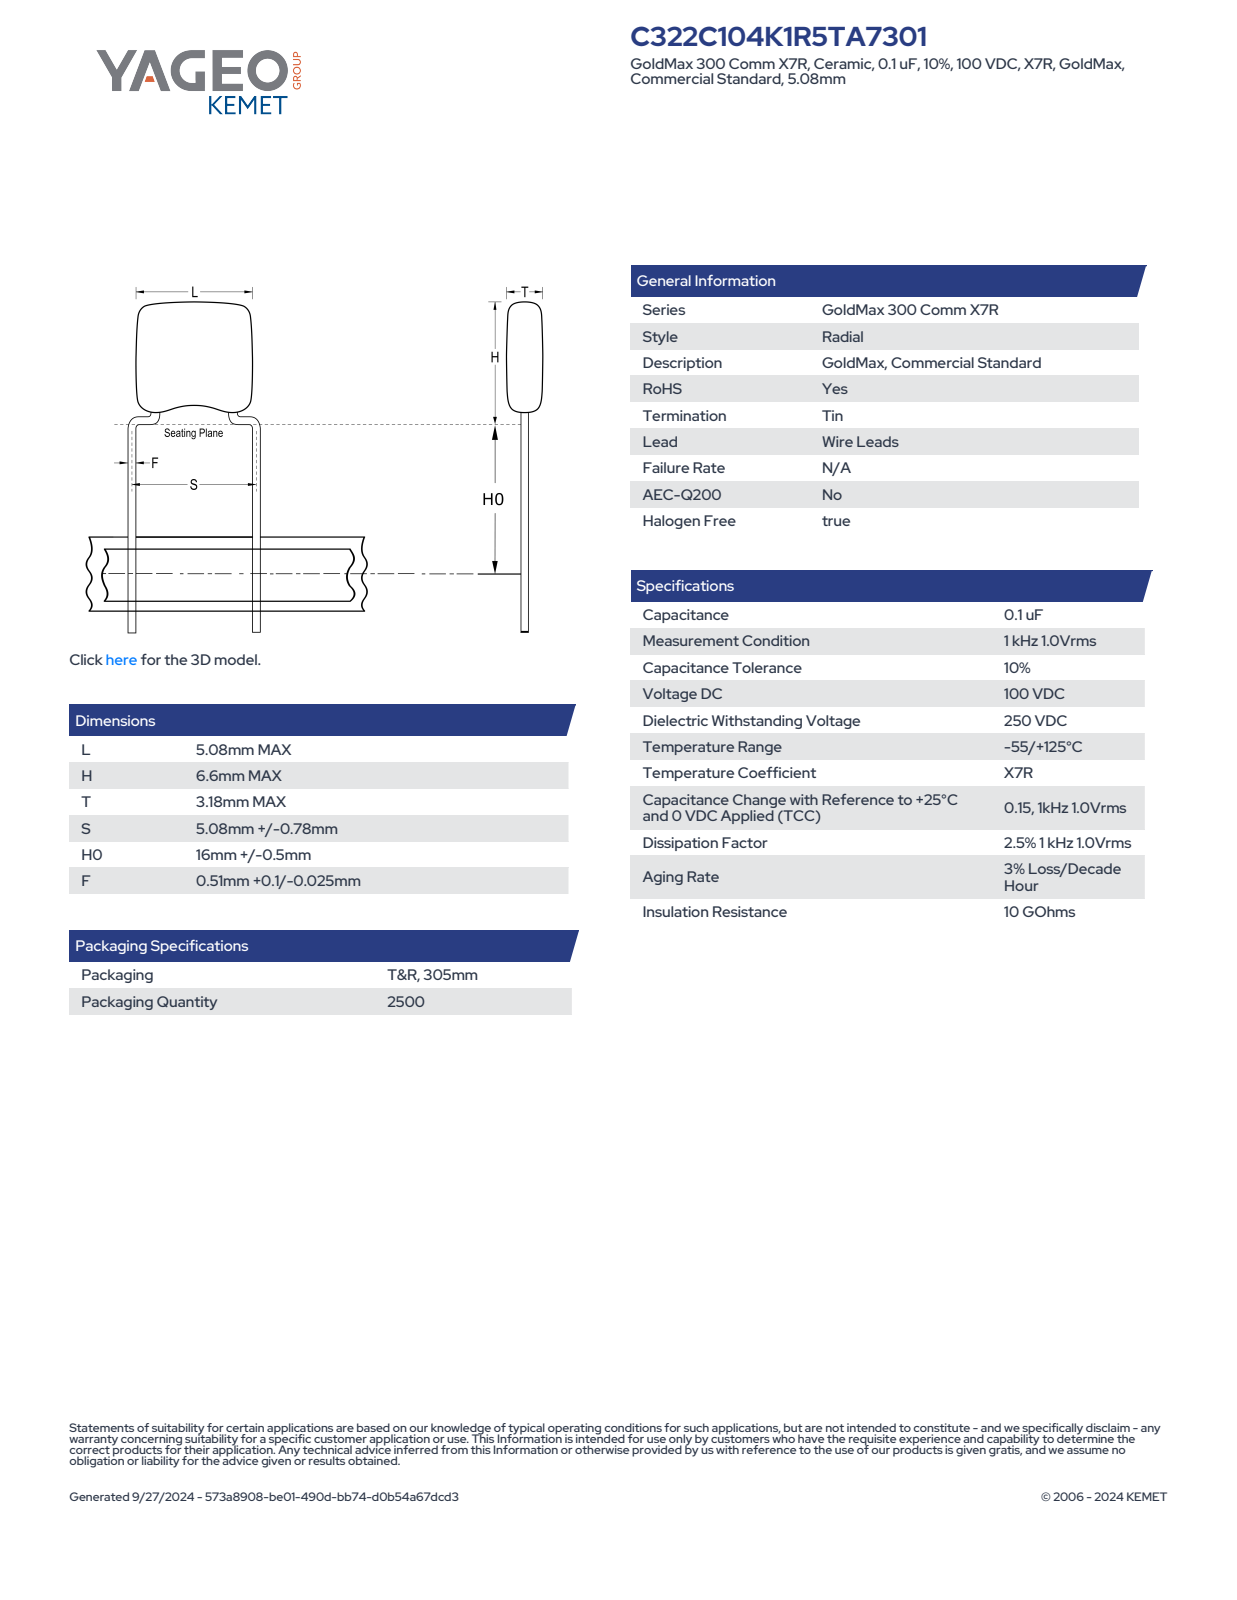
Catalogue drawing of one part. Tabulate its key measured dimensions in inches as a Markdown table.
| quantity | value |
| --- | --- |
| part name | CCR_SB_5.08X6.6_L5.08H6.6T3.18S5.08H016.5F0.51 |
| STEP written by | SolidWorks 2014 (AUTOMOTIVE_DESIGN) |
| units | inches |
| bodies | 4 solids, 97 faces (65 planar, 14 cylindrical, 18 other) |
| overall size | 0.909 × 0.22 × 0.126 |
| volume | 0.005 in³ |
| surface area | 0.237 in² |
| round bosses / shafts (diameter × count) | 0.02 × 2 |
| partial cylindrical surfaces (radius × count) | 0.039 × 10 |
| main face-to-face distances | 0.125, 0.2, 0.189, 0.126, 0.017, 0.102, 0.087, 0.085, 0.104, 0.015 |
